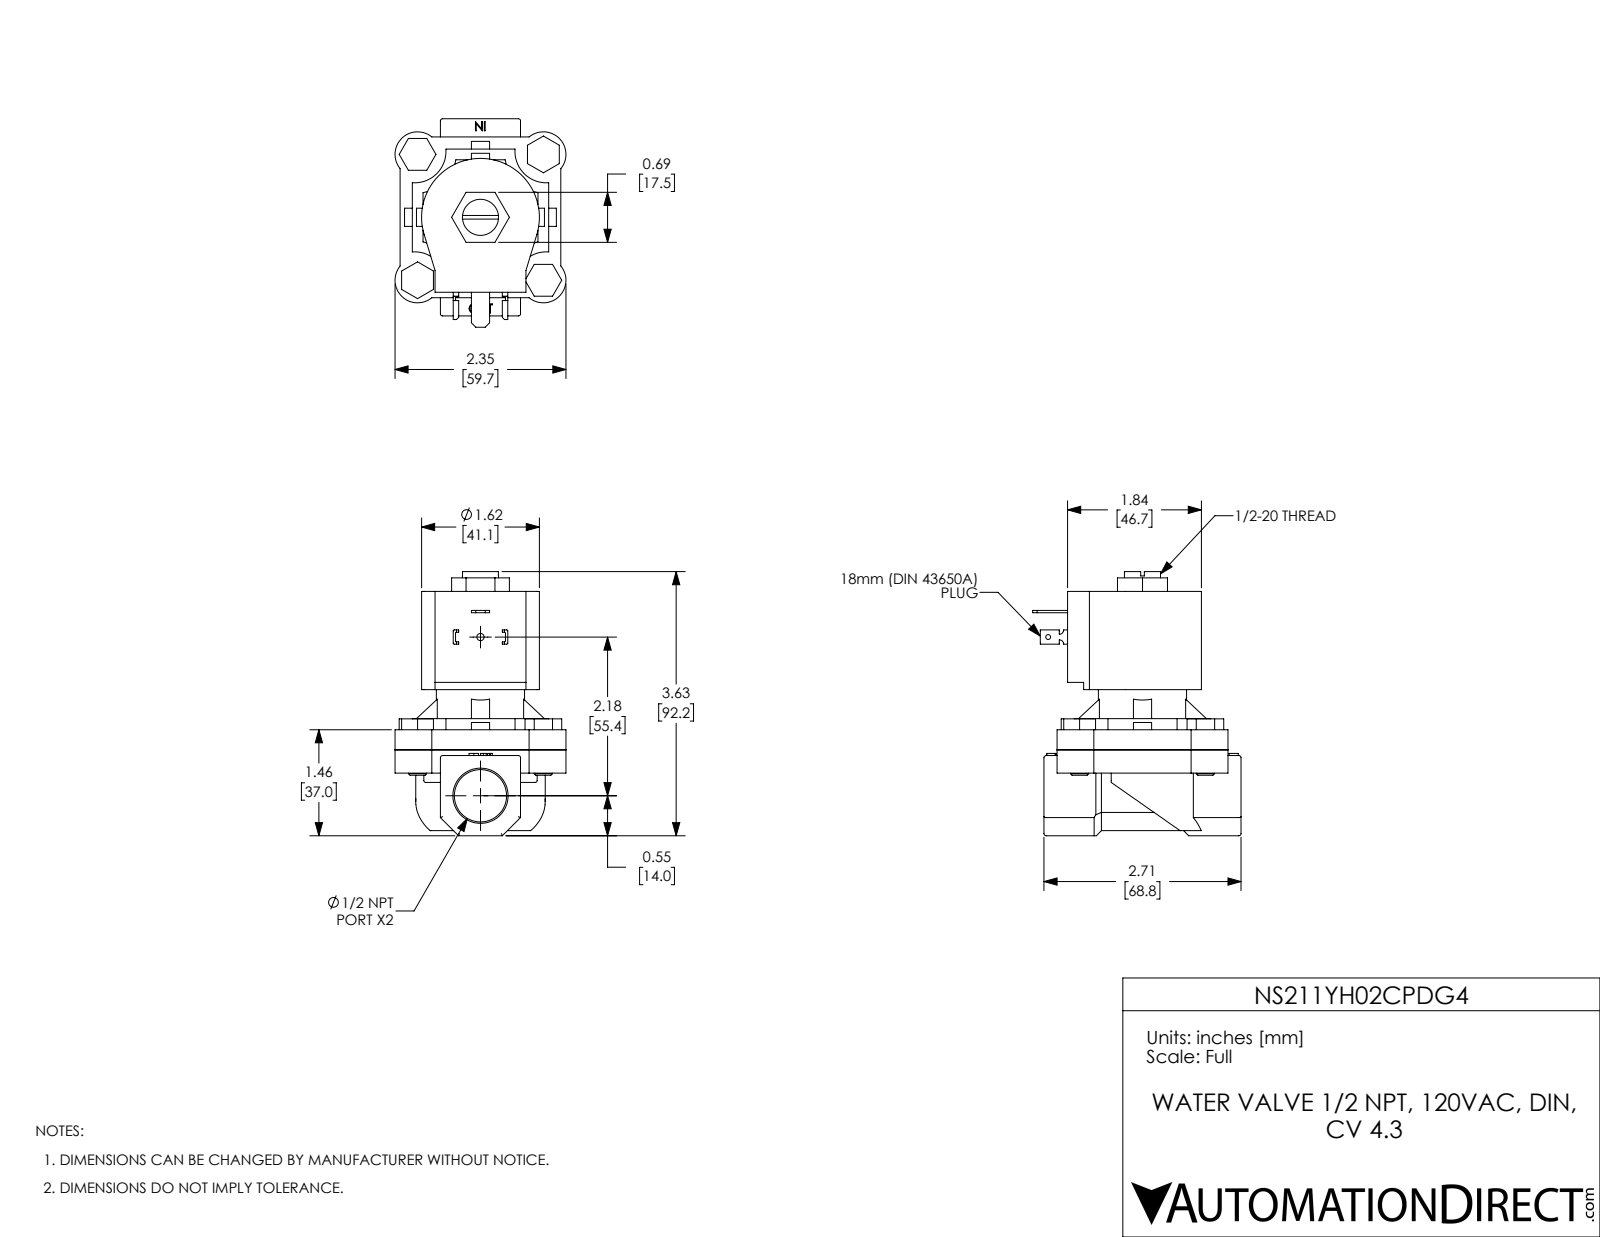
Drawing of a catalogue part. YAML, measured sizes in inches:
part_name: "NS211YH02CPDG4"
step_written_by: "SolidWorks 2024 (CONFIG_CONTROL_DESIGN)"
units: inches
bodies: {solids: 11, faces: 385, planar: 239, cylindrical: 113, other: 33}
overall_size: [3.63, 2.865, 2.35]
volume: 9.473
surface_area: 65.14
round_holes:
  - {diameter: 0.25, count: 4}
  - {diameter: 0.067, count: 1}
  - {diameter: 0.1, count: 1}
  - {diameter: 0.496, count: 1}
  - {diameter: 0.512, count: 1}
  - {diameter: 0.719, count: 1}
  - {diameter: 1.155, count: 1}
round_bosses_or_shafts:
  - {diameter: 0.248, count: 4}
  - {diameter: 1.213, count: 1}
partial_cylinders:
  - {radius: 0.03, count: 15}
  - {radius: 0.015, count: 8}
  - {radius: 0.31, count: 4}
  - {radius: 0.432, count: 4}
  - {radius: 0.579, count: 4}
  - {radius: 0.06, count: 2}
  - {radius: 0.81, count: 1}
  - {radius: 0.89, count: 1}
face_to_face_distances: [0.276, 2.177, 1.901, 0.32, 0.596, 2.497, 0.554, 1.656, 0.25, 1.147]
hole_center_spacings: [1.223, 1.73, 2.446, 2.181]
